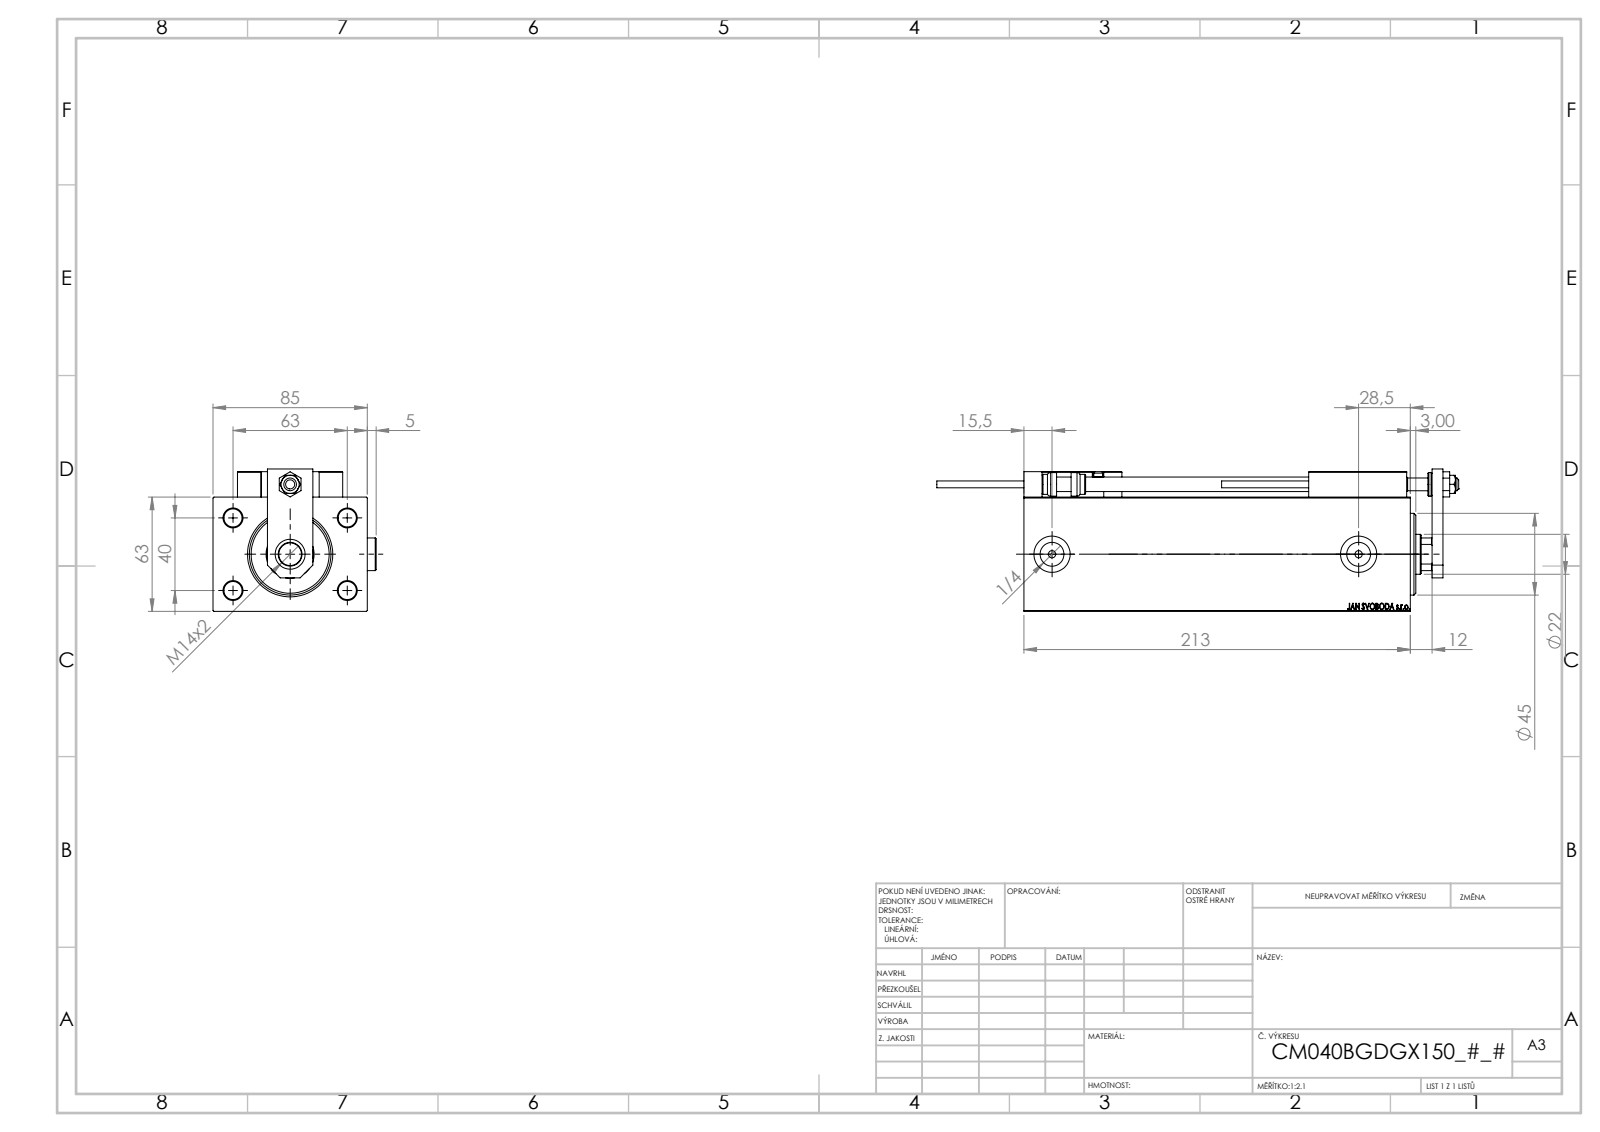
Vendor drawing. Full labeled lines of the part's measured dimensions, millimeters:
Part name (STEP PRODUCT): Zatka_OIL_PORT; ZARAZKA; V450CM_VC_B; SWITCH_X_FRONT_BACK (+7 more)
STEP written by: SolidWorks 2019 (CONFIG_CONTROL_DESIGN)
Units: millimetres
Bodies: 26 solids, 1372 faces (595 planar, 200 cylindrical, 577 other)
Overall size (bounding box): 287.7 × 89.9 × 78.5
Volume: 1 050 000 mm³ · Surface area: 161 893 mm²
Round holes (diameter × count): ⌀4 ×6, ⌀8 ×5, ⌀3.2 ×4, ⌀10 ×4, ⌀5 ×2, ⌀13.16 ×2, ⌀20 ×2, ⌀7 ×1, ⌀12.5 ×1, ⌀16.5 ×1, ⌀22 ×1, ⌀25.5 ×1
Round bosses / shafts (diameter × count): ⌀18 ×2, ⌀5 ×2, ⌀3.8 ×2, ⌀13 ×1, ⌀11 ×1
Partial cylindrical surfaces — rounded edges, fillets, slot ends (radius × count): R0.3 ×30, R3 ×2, R10.5 ×1
Main face-to-face distances: 63, 85, 12, 213, 201, 14, 77, 18, 30, 13.5
Hole centre spacings: 37.31, 11.37, 20, 29.59, 29.69, 36.06, 36.53, 40
